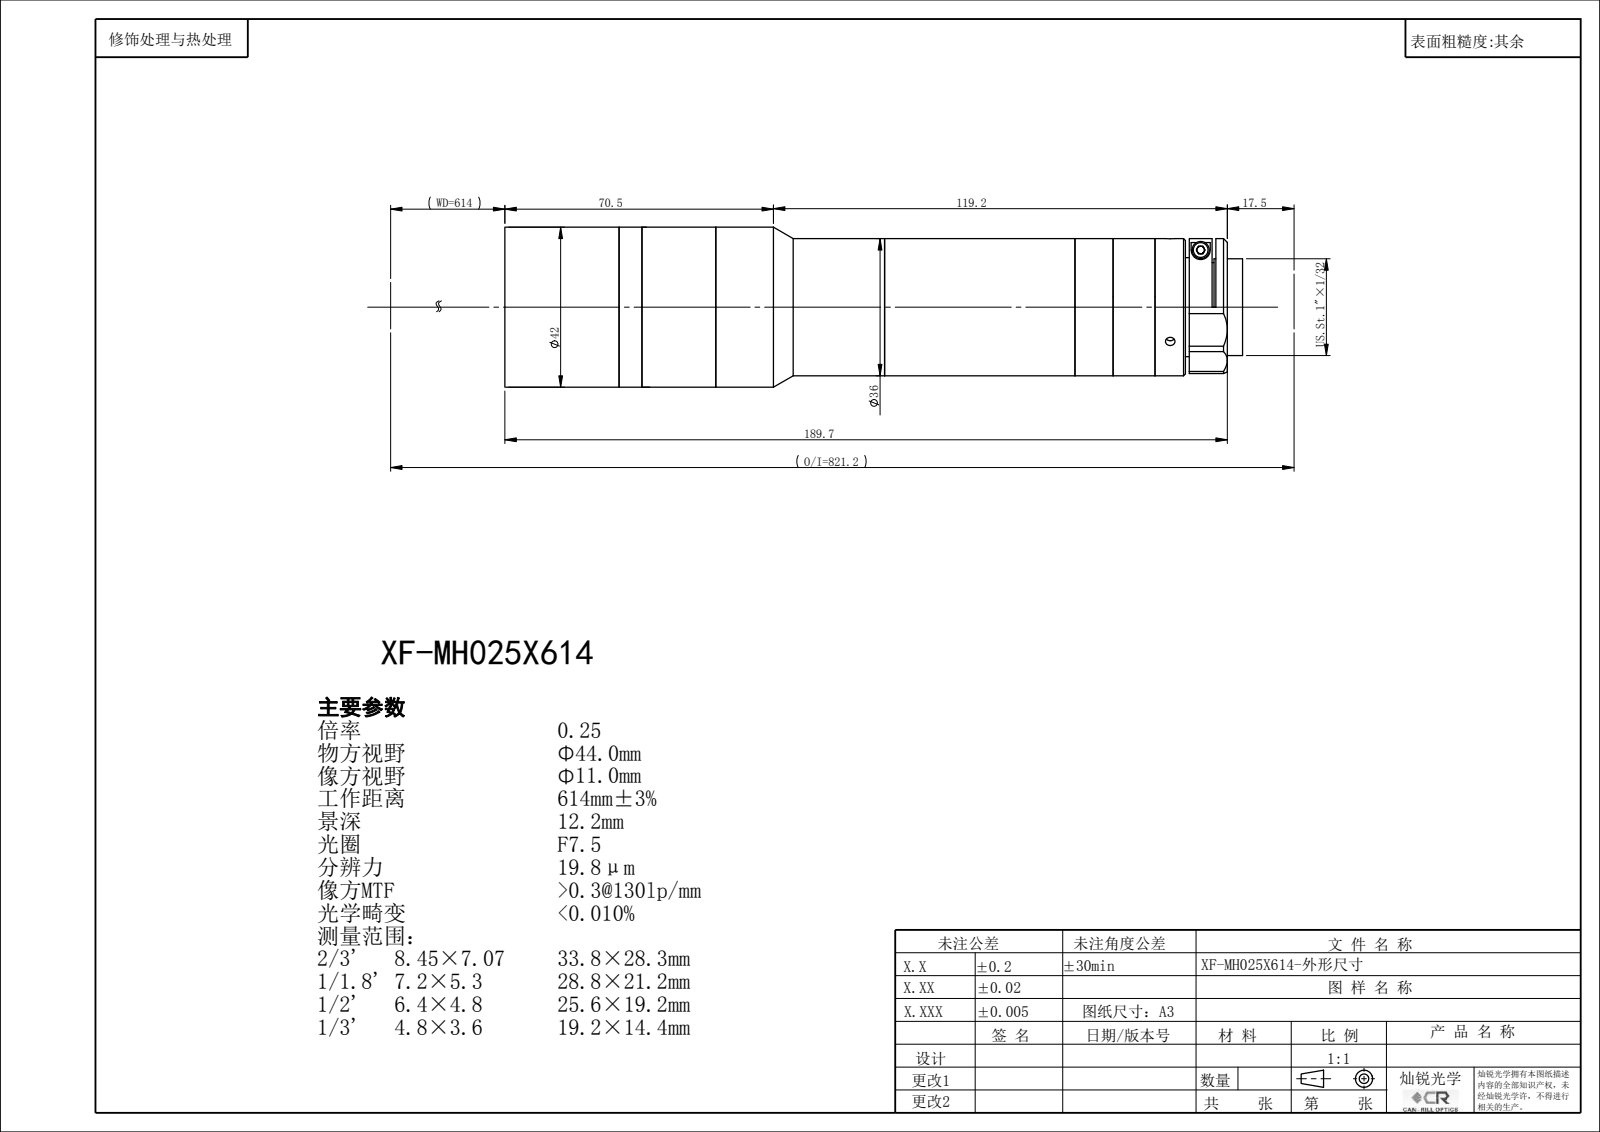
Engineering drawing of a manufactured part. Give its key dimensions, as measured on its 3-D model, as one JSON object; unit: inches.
{"part_name": "XF-MH025X614", "step_written_by": "SolidWorks 2022 (CONFIG_CONTROL_DESIGN)", "units": "inches", "bodies": {"solids": 0, "faces": 134, "planar": 70, "cylindrical": 42, "other": 22}, "overall_size": [7.617, 1.654, 1.654], "round_holes": [[0.098, 3], [0.882, 1], [0.945, 1], [1.299, 1], [1.433, 1]], "round_bosses_or_shafts": [[1.654, 1], [1.417, 1], [1.339, 1], [1, 1]], "face_to_face_distances": [0.739, 0.059, 0.68, 6.721, 7.401, 7.46, 5.894, 6.288, 0.433, 1.113]}
